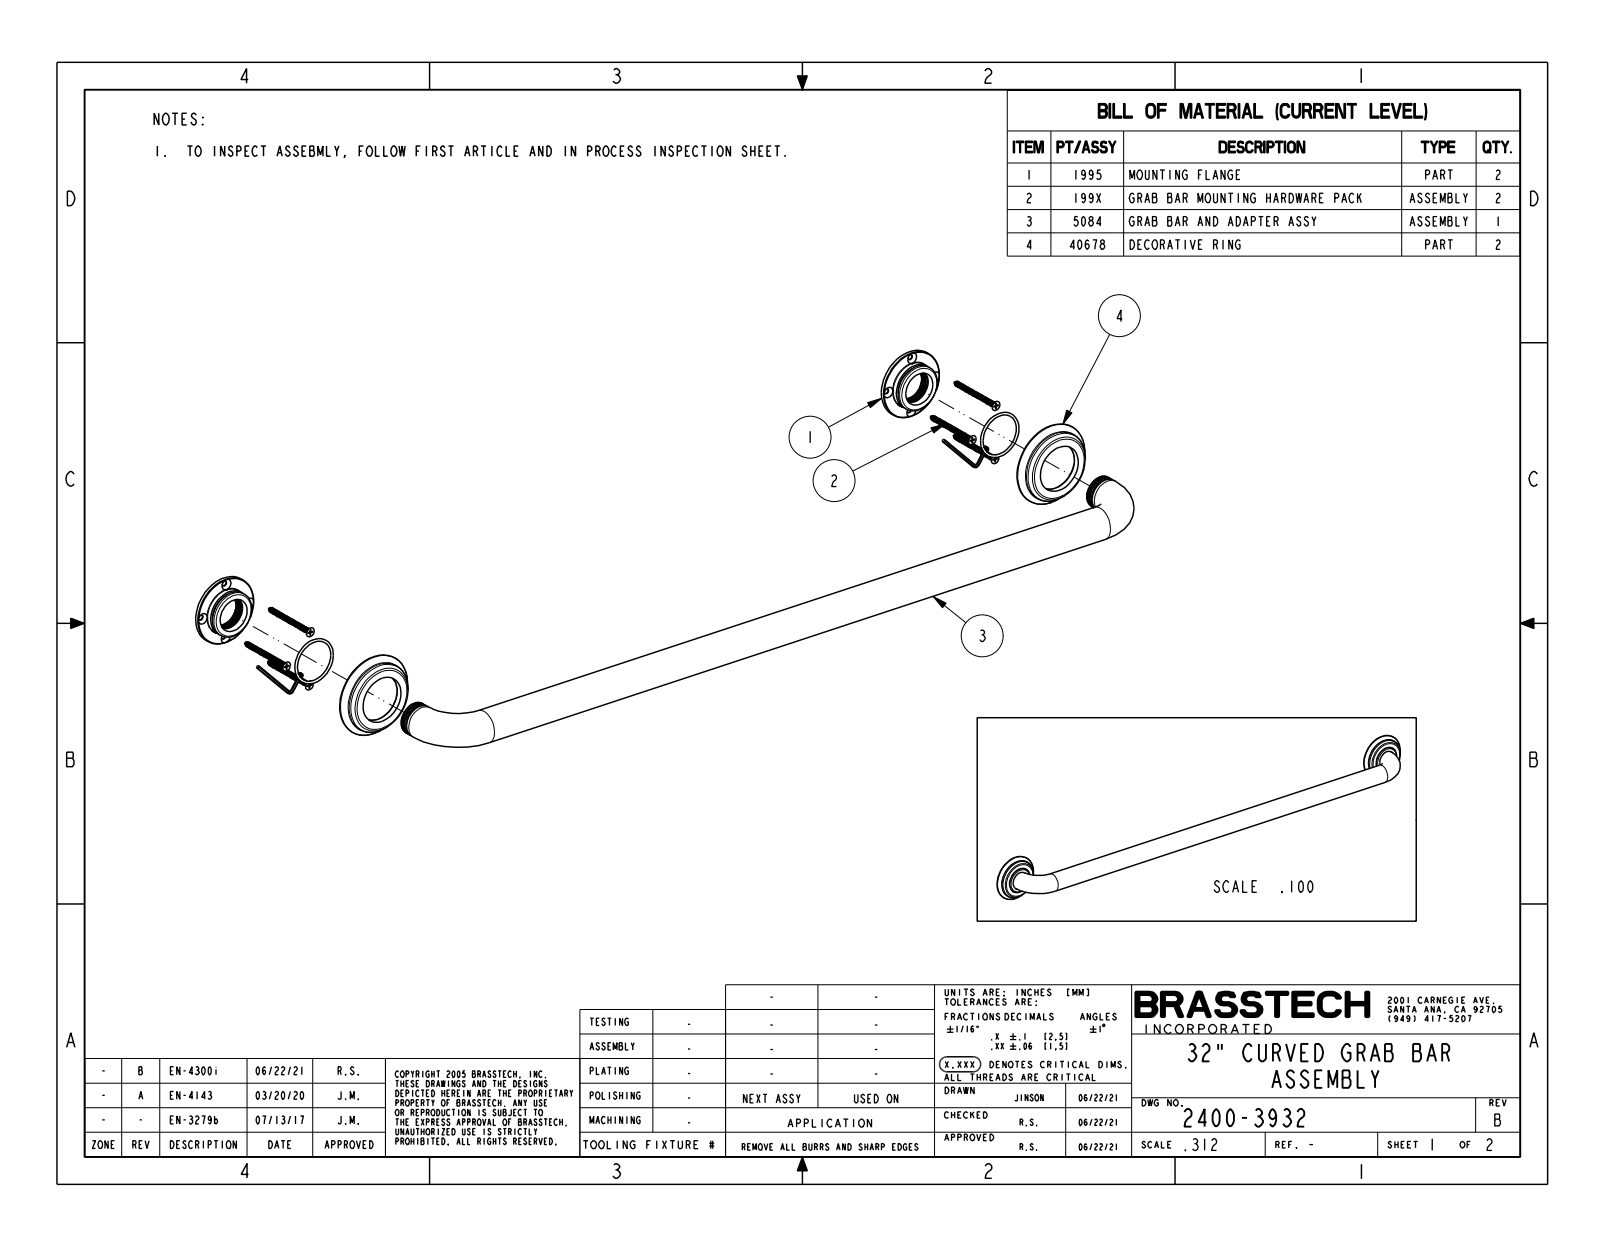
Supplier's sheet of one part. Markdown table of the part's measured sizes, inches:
| quantity | value |
| --- | --- |
| part name | 2400-3932 |
| STEP written by | CREO PARAMETRIC BY PTC INC, 2018400 (CONFIG_CONTROL_DESIGN) |
| units | inches |
| bodies | 1 solid, 72 faces (14 planar, 30 cylindrical, 28 other) |
| overall size | 35 × 3 × 2.755 |
| volume | 52.82 in³ |
| surface area | 183.4 in² |
| round bosses / shafts (diameter × count) | 1.25 × 3, 1.75 × 2 |
| partial cylindrical surfaces (radius × count) | 0.125 × 8, 0.05 × 6 |
| main face-to-face distances | 0.53, 3, 32, 0.6, 0.07, 35, 29 |
